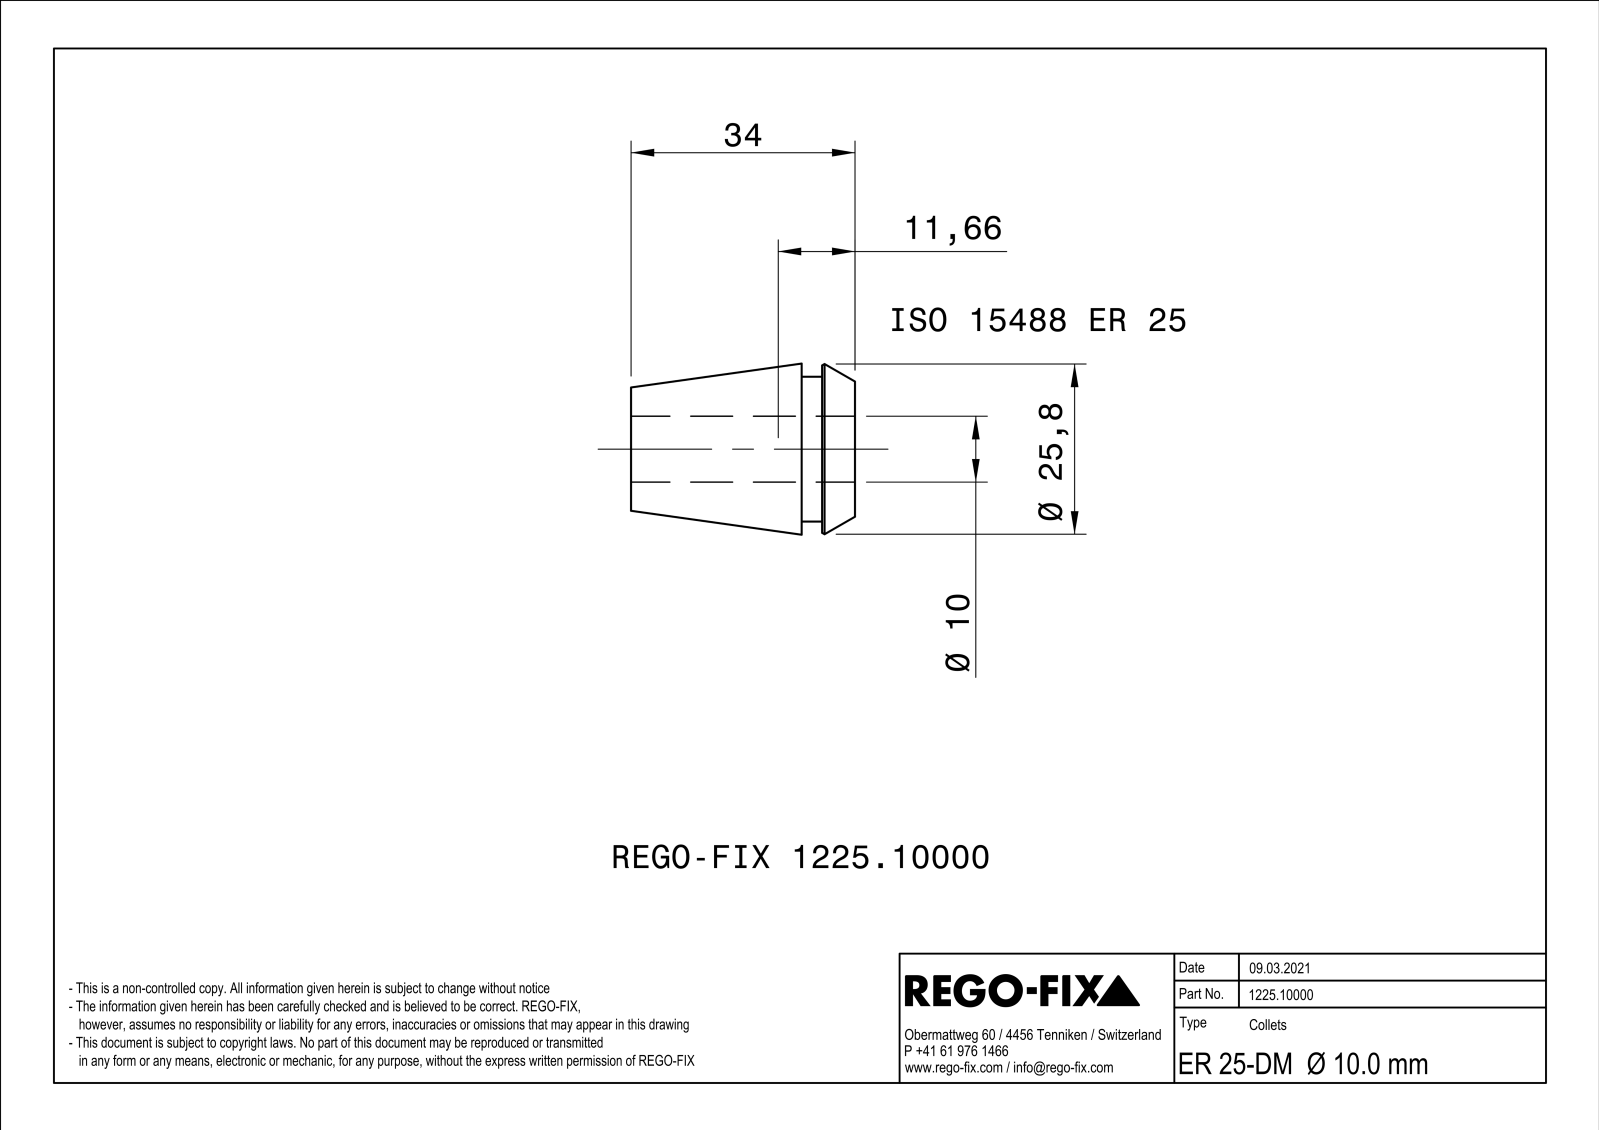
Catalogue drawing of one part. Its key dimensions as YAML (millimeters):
part_name: "NOCUT"
step_written_by: "SIEMENS PLM Software Solid Edge ST10 (AUTOMOTIVE_DESIGN)"
units: millimeters
bodies: {solids: 1, faces: 154, planar: 80, cylindrical: 9, other: 65}
overall_size: [34, 25.99, 25.99]
volume: 9025
surface_area: 8374
round_holes:
  - {diameter: 10, count: 1}
round_bosses_or_shafts:
  - {diameter: 22, count: 1}
face_to_face_distances: [0.8, 34, 5, 29, 8.1, 25.9, 3.1, 15, 10, 6.9]
